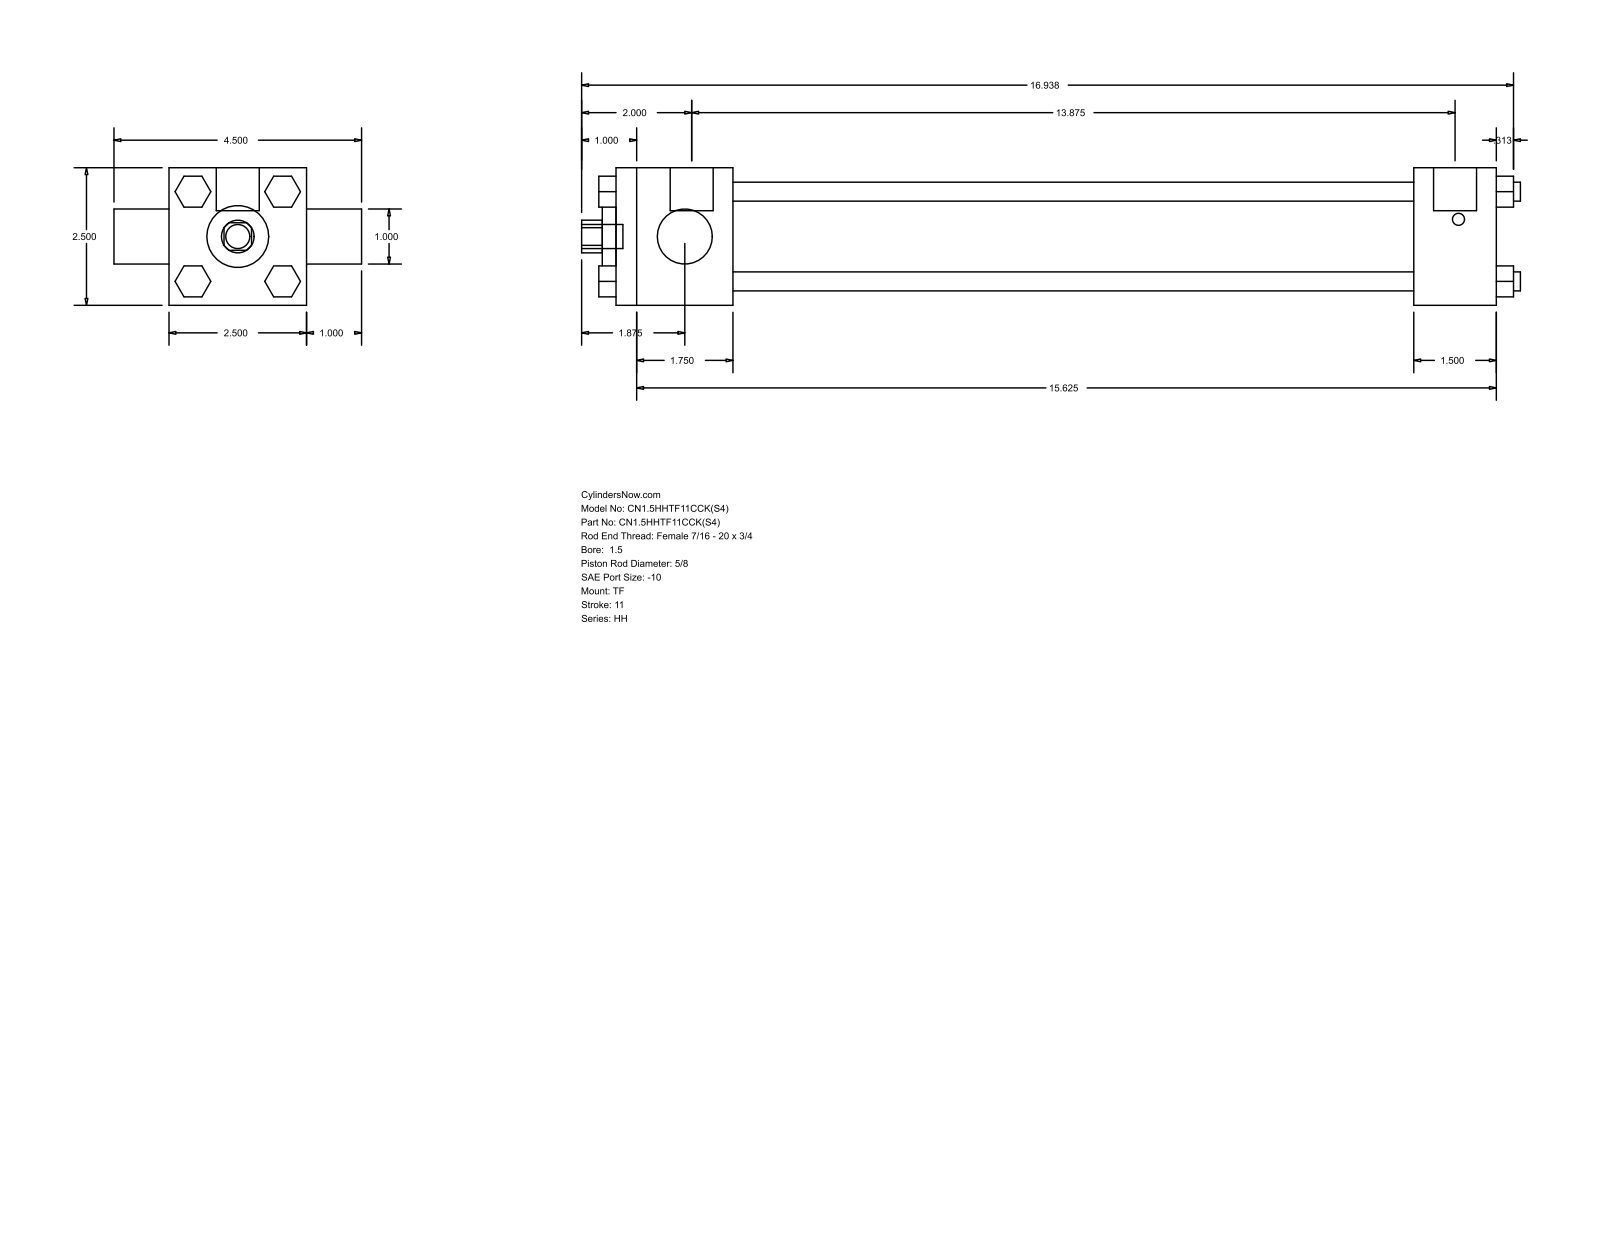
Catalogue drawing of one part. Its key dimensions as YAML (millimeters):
part_name: "HH_TF__0150_0.625"
step_written_by: "GSSL Pune (CONFIG_CONTROL_DESIGN)"
units: millimeters
bodies: {solids: 0, faces: 120, planar: 92, cylindrical: 28, other: 0}
overall_size: [433.39, 114.3, 63.5]
round_holes:
  - {diameter: 15.88, count: 1}
  - {diameter: 25.4, count: 1}
  - {diameter: 28.57, count: 1}
  - {diameter: 44.45, count: 1}
round_bosses_or_shafts:
  - {diameter: 8.76, count: 4}
  - {diameter: 5.56, count: 3}
  - {diameter: 19.84, count: 2}
  - {diameter: 11.11, count: 1}
partial_cylinders:
  - {radius: 7.54, count: 1}
face_to_face_distances: [63.5, 406.39, 53.97, 352.42, 368.3, 314.33, 38.09, 25.4, 20.7, 14.29]
